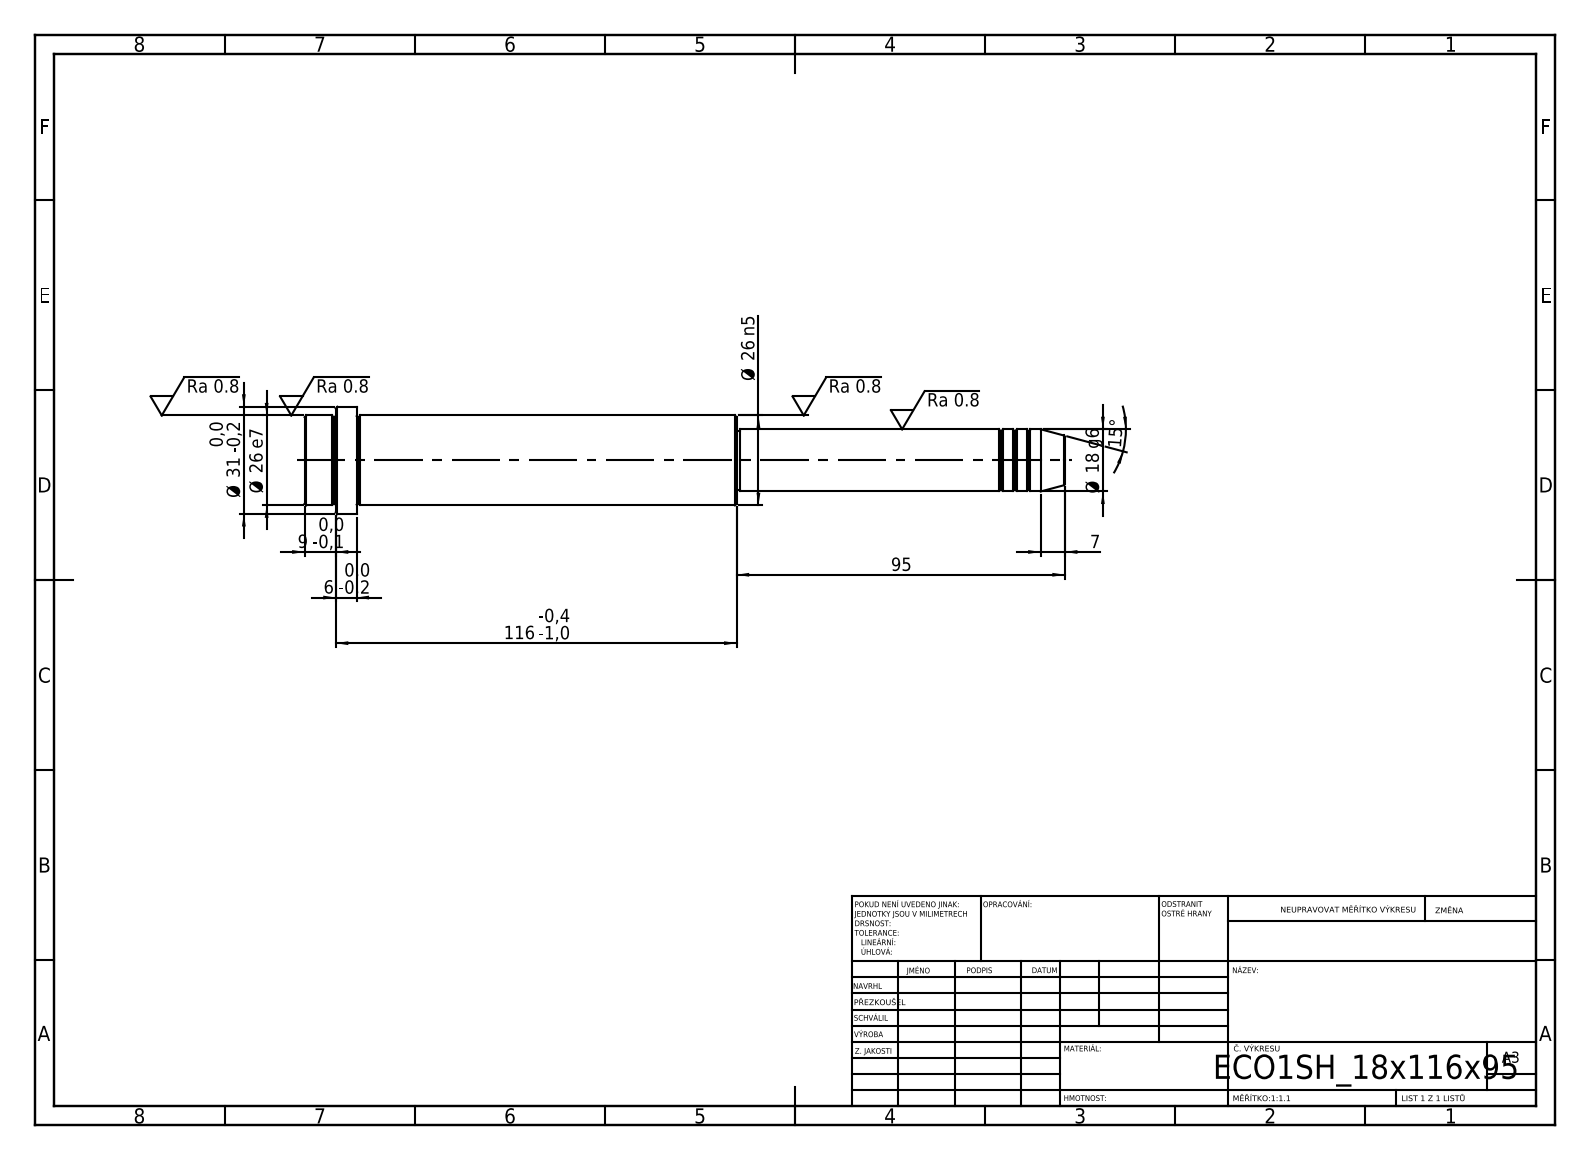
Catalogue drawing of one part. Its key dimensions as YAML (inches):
step_written_by: "SolidWorks 2019 (CONFIG_CONTROL_DESIGN)"
units: inches
bodies: {solids: 1, faces: 52, planar: 6, cylindrical: 16, other: 30}
overall_size: [8.661, 1.22, 1.22]
volume: 5.574
surface_area: 26.67
round_bosses_or_shafts:
  - {diameter: 1.22, count: 1}
  - {diameter: 1.024, count: 1}
  - {diameter: 0.709, count: 1}
  - {diameter: 0.669, count: 1}
face_to_face_distances: [4.921, 4.331, 0.591, 4.567, 0.236, 0.354, 3.74, 8.071, 8.307, 8.661]
